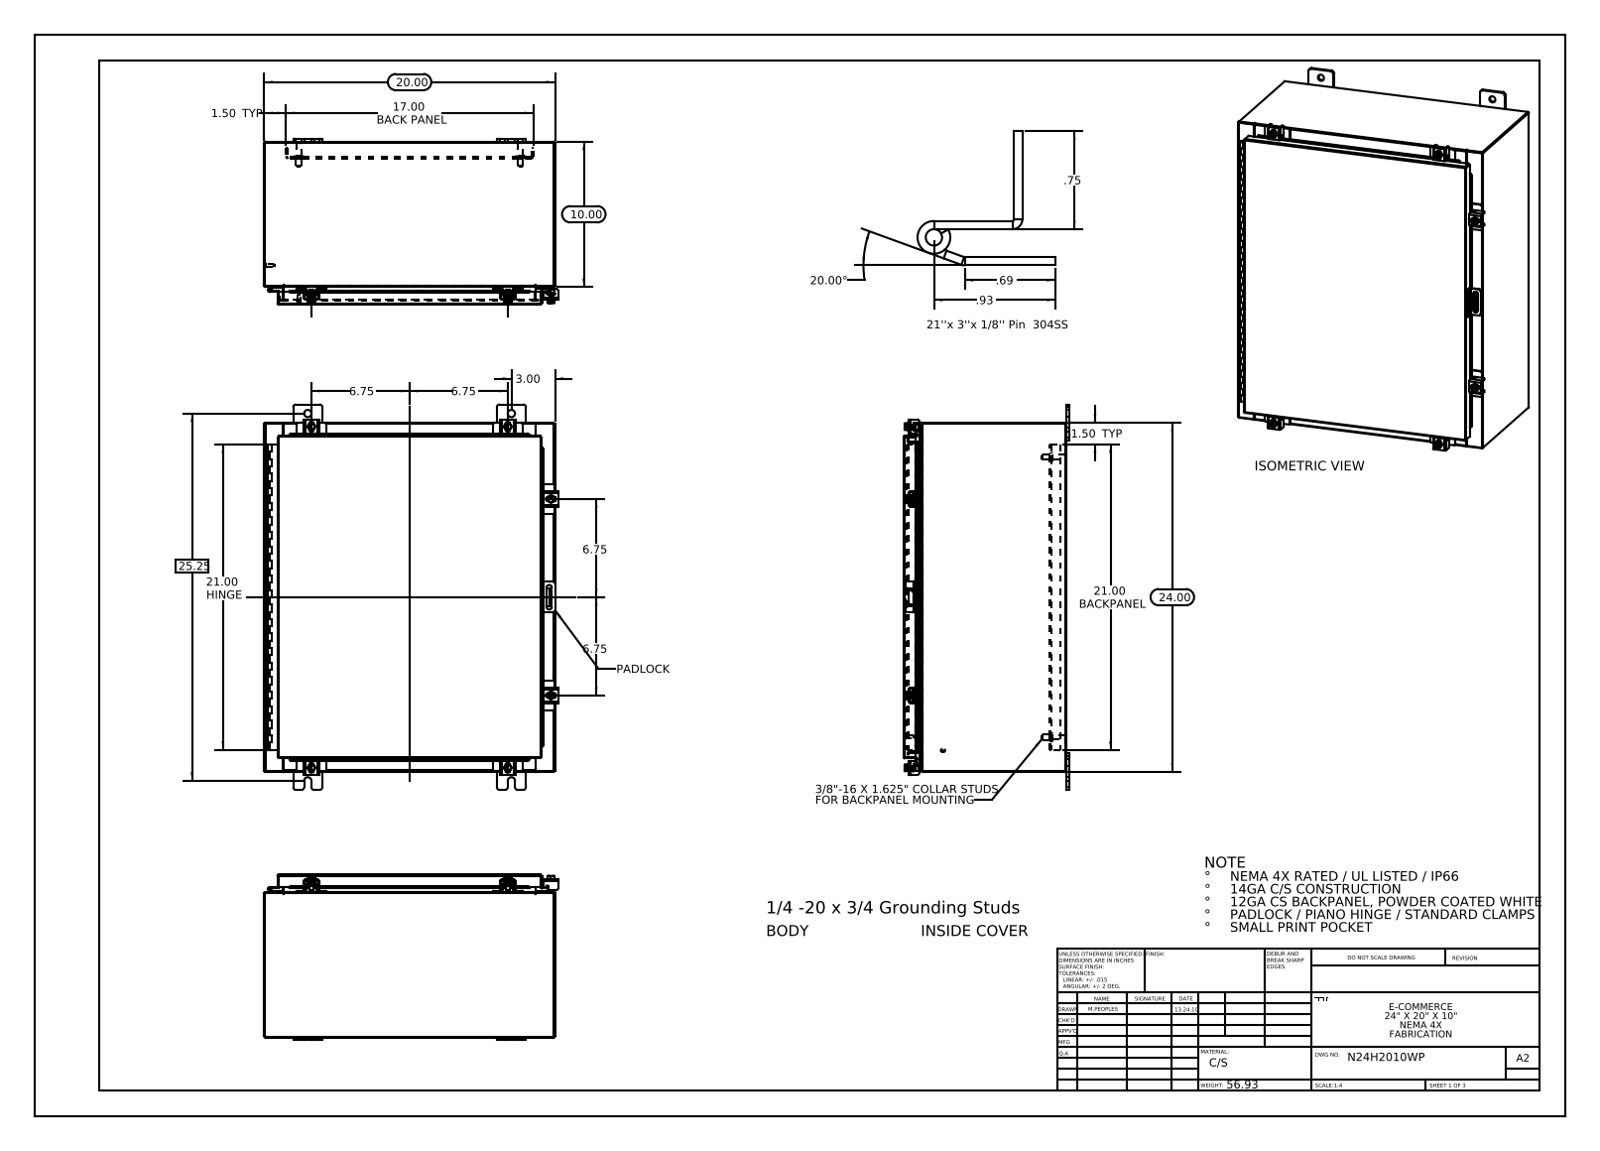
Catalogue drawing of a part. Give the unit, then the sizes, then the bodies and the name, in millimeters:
Units: millimetres
Overall size (bounding box): 673.1 × 513.4 × 289.3
Round holes (diameter × count): ⌀12.7 ×8, ⌀5.4 ×6, ⌀6.6 ×6, ⌀3.2 ×2
Round bosses / shafts (diameter × count): ⌀6.4 ×7, ⌀12.7 ×6, ⌀10.1 ×6, ⌀15.9 ×4, ⌀9.5 ×4, ⌀8.4 ×4, ⌀8 ×2, ⌀6 ×2
Partial cylindrical surfaces — rounded edges, fillets, slot ends (radius × count): R1.5 ×30, R0.3 ×25, R4.8 ×24, R2.2 ×21, R3 ×12, R3.6 ×12, R3.2 ×10, R1.3 ×9
Main face-to-face distances: 1.9, 282.6, 506.1, 280.7, 284.5, 607.7, 2.6, 25.4, 27.3, 255.3
Hole centre spacings: 542.8, 653.8, 342.9, 10.9, 23.7, 47.2, 57.8, 57.8
Volume: 3 279 000 mm³ · Surface area: 3 267 000 mm²
Bodies: 49 solids, 1735 faces (914 planar, 713 cylindrical, 108 other)
Part name (STEP PRODUCT): N24H2010WP; N24H2010SSWP 22101002; N24H2010SSWP Top; N24H2010SSWP 125 Pin Hinge (+8 more)
STEP written by: SolidWorks 2013 (CONFIG_CONTROL_DESIGN)
